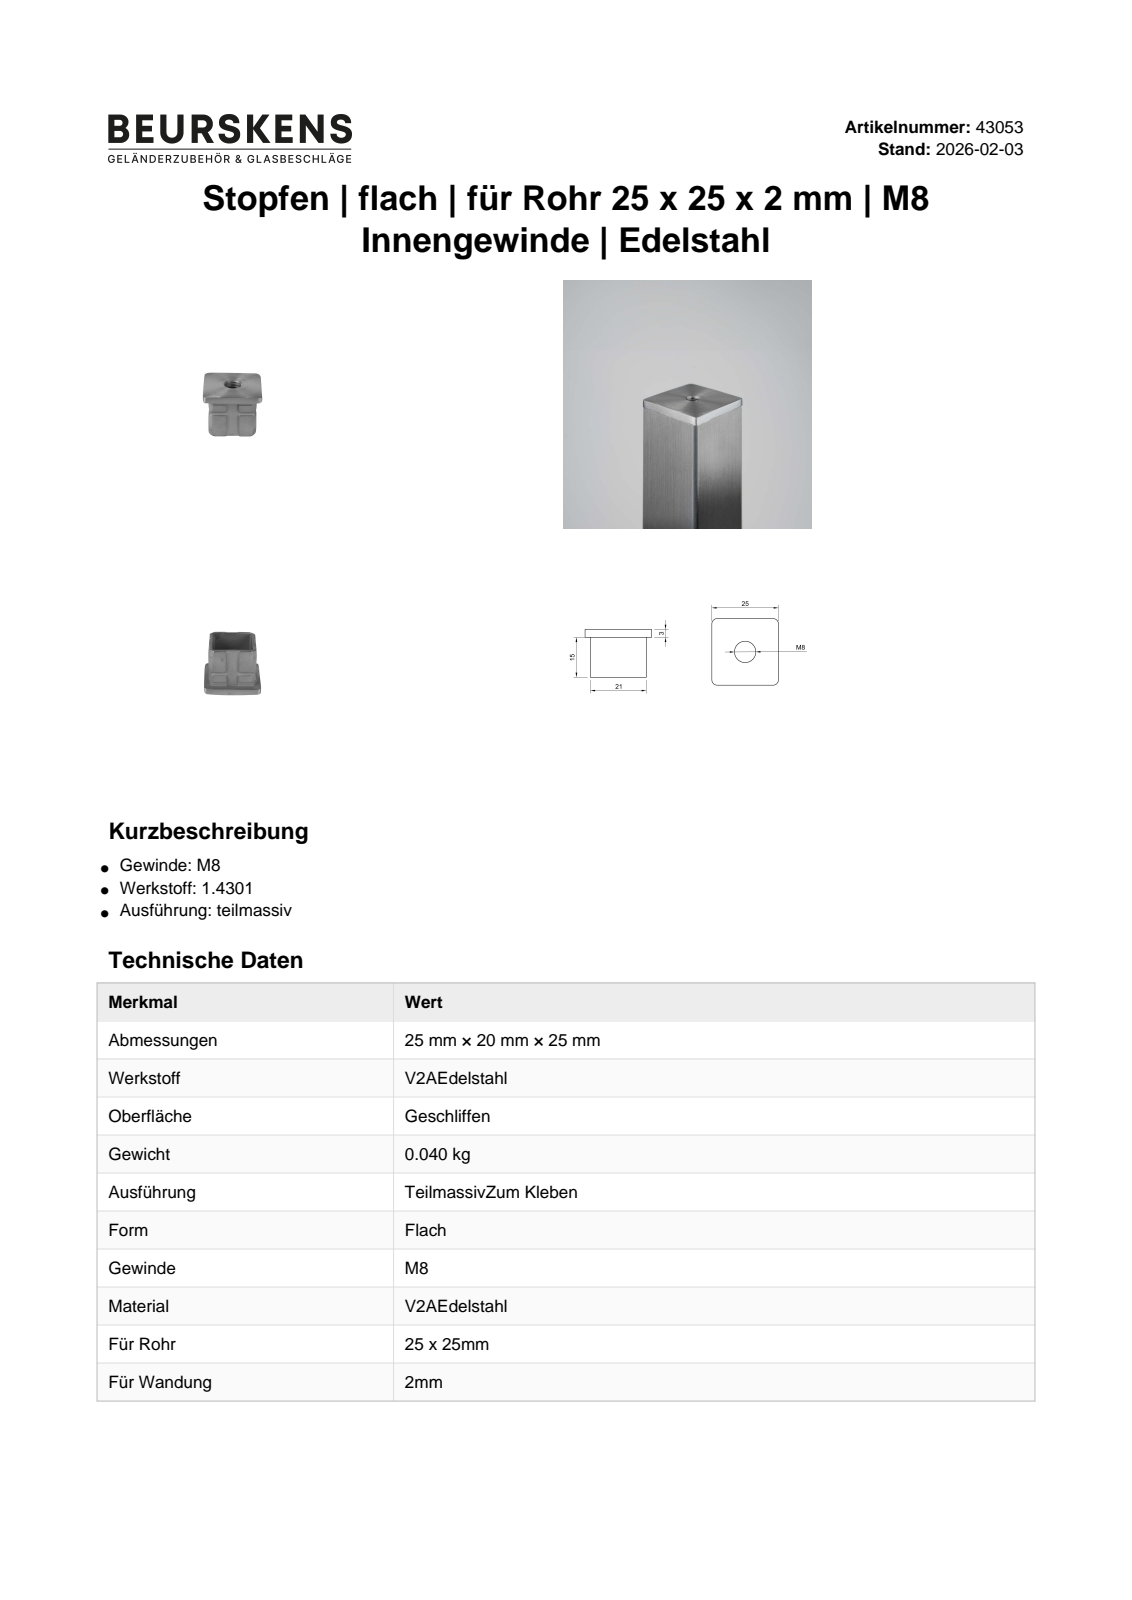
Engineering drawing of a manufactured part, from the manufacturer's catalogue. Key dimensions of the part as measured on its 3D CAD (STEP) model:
Part name (STEP PRODUCT): 43053
STEP written by: Autodesk Inventor 2022 (AUTOMOTIVE_DESIGN)
Units: millimetres
Bodies: 1 solid, 27 faces (17 planar, 10 cylindrical, 0 other)
Overall size (bounding box): 25 × 25 × 18
Volume: 4 062 mm³ · Surface area: 4 257 mm²
Round holes (diameter × count): ⌀8 ×1
Round bosses / shafts (diameter × count): ⌀11 ×1
Partial cylindrical surfaces — rounded edges, fillets, slot ends (radius × count): R2 ×8
Main face-to-face distances: 2, 19, 21, 17, 4, 23, 1, 3, 15, 16
